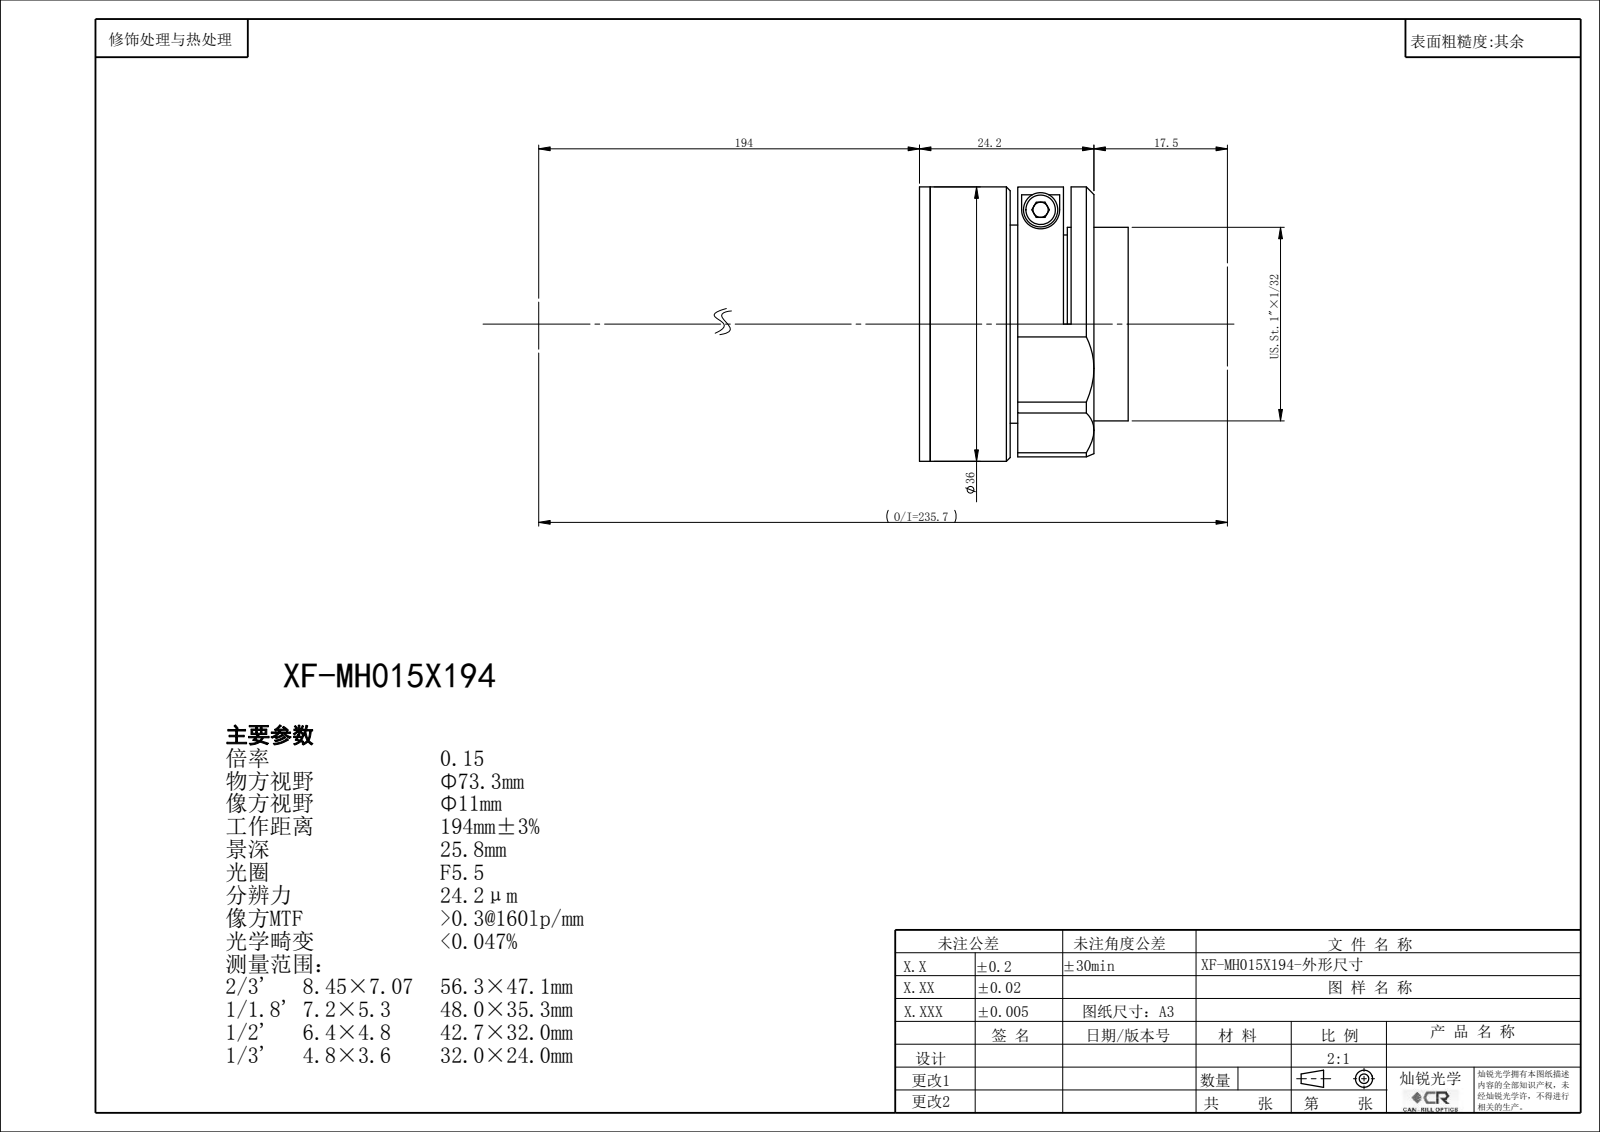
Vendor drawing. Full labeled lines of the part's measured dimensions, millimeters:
Part name (STEP PRODUCT): XF-MH015X194
STEP written by: SolidWorks 2022 (CONFIG_CONTROL_DESIGN)
Units: millimetres
Bodies: 0 solids, 99 faces (47 planar, 40 cylindrical, 12 other)
Overall size (bounding box): 36 × 36 × 28.21
Round holes (diameter × count): ⌀2.5 ×3, ⌀8 ×1, ⌀9 ×1, ⌀10.4 ×1, ⌀13 ×1, ⌀17 ×1, ⌀21 ×1, ⌀21.5 ×1, ⌀24.9 ×1, ⌀26 ×1
Round bosses / shafts (diameter × count): ⌀36 ×1, ⌀34 ×1, ⌀29 ×1, ⌀25.4 ×1, ⌀24 ×1
Main face-to-face distances: 22.81, 1.4, 24.21, 22.71, 20.4, 1.5, 21.31, 4.5, 1, 2
